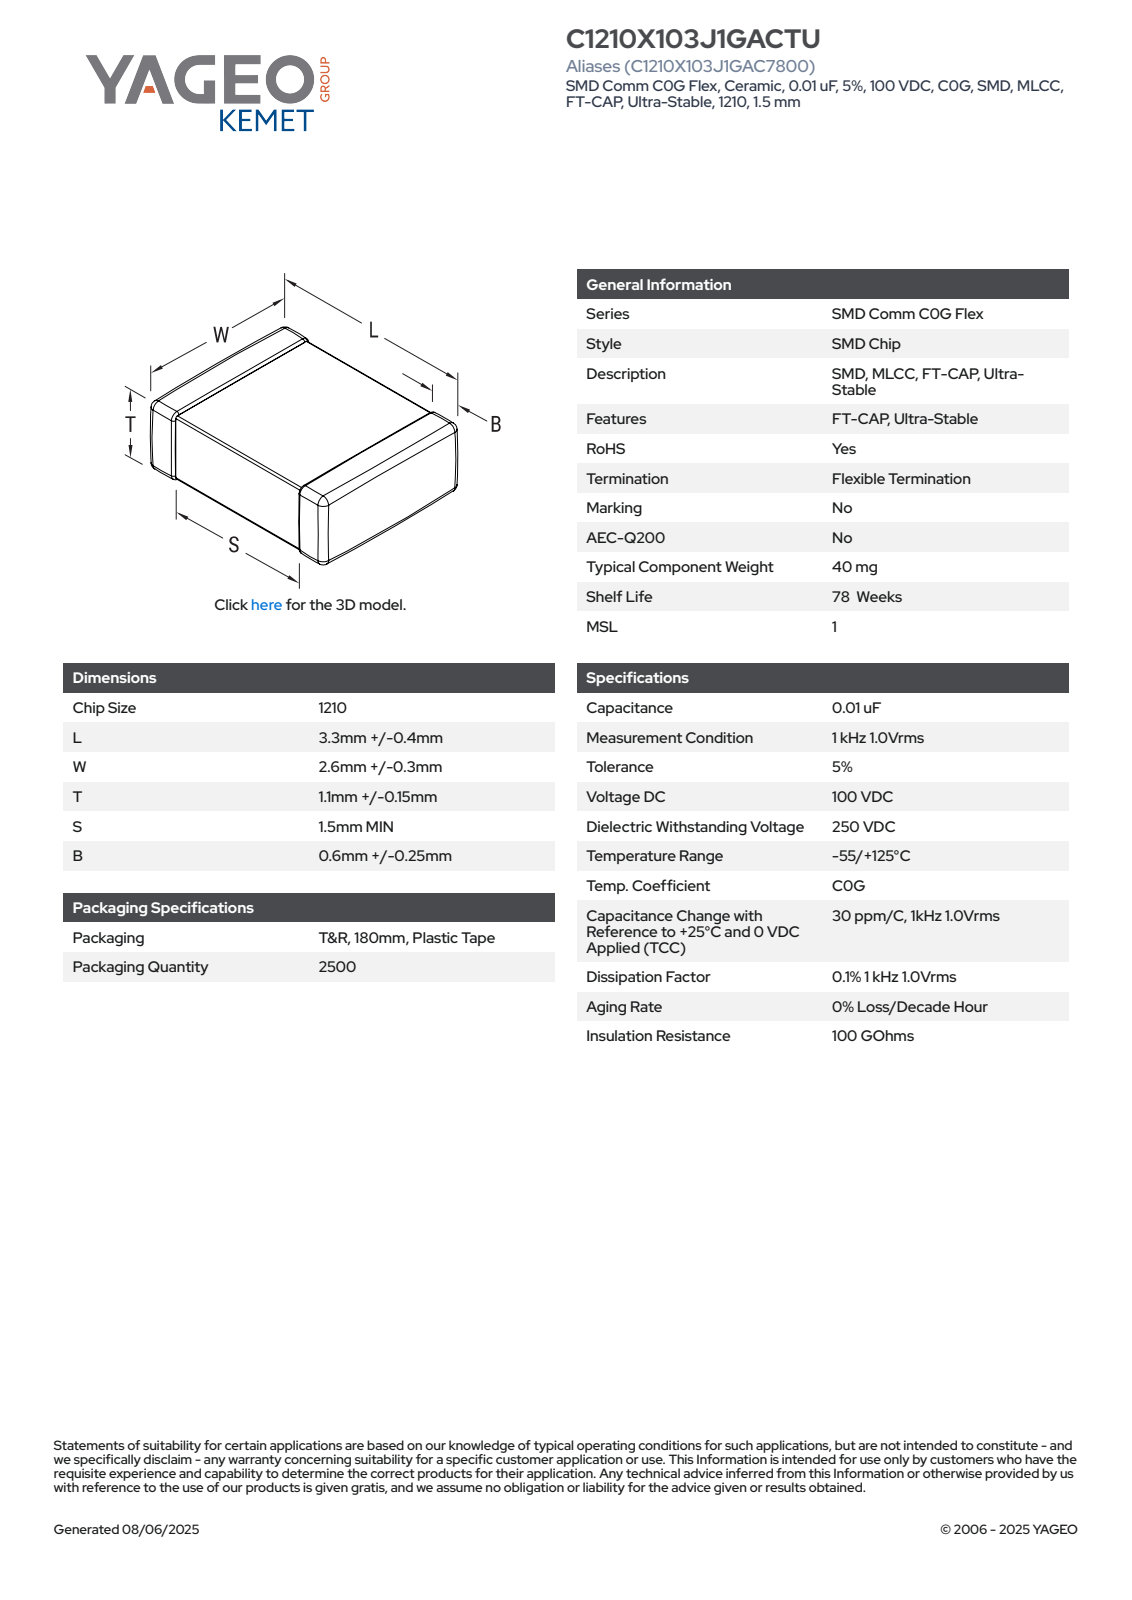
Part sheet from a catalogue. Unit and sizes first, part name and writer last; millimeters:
Units: millimetres
Overall size (bounding box): 3.7 × 2.9 × 1.25
Main face-to-face distances: 1.19, 1.13, 1.25, 2.84, 3.7, 2.78, 2.9, 0.43, 1.57, 2.13
Volume: 12 mm³ · Surface area: 38 mm²
Bodies: 4 solids, 125 faces (71 planar, 38 cylindrical, 16 other)
Part name (STEP PRODUCT): CCS_CCSTD_1210_L3.7W2.9T1.25B0.6
STEP written by: SolidWorks 2021 (AUTOMOTIVE_DESIGN)
